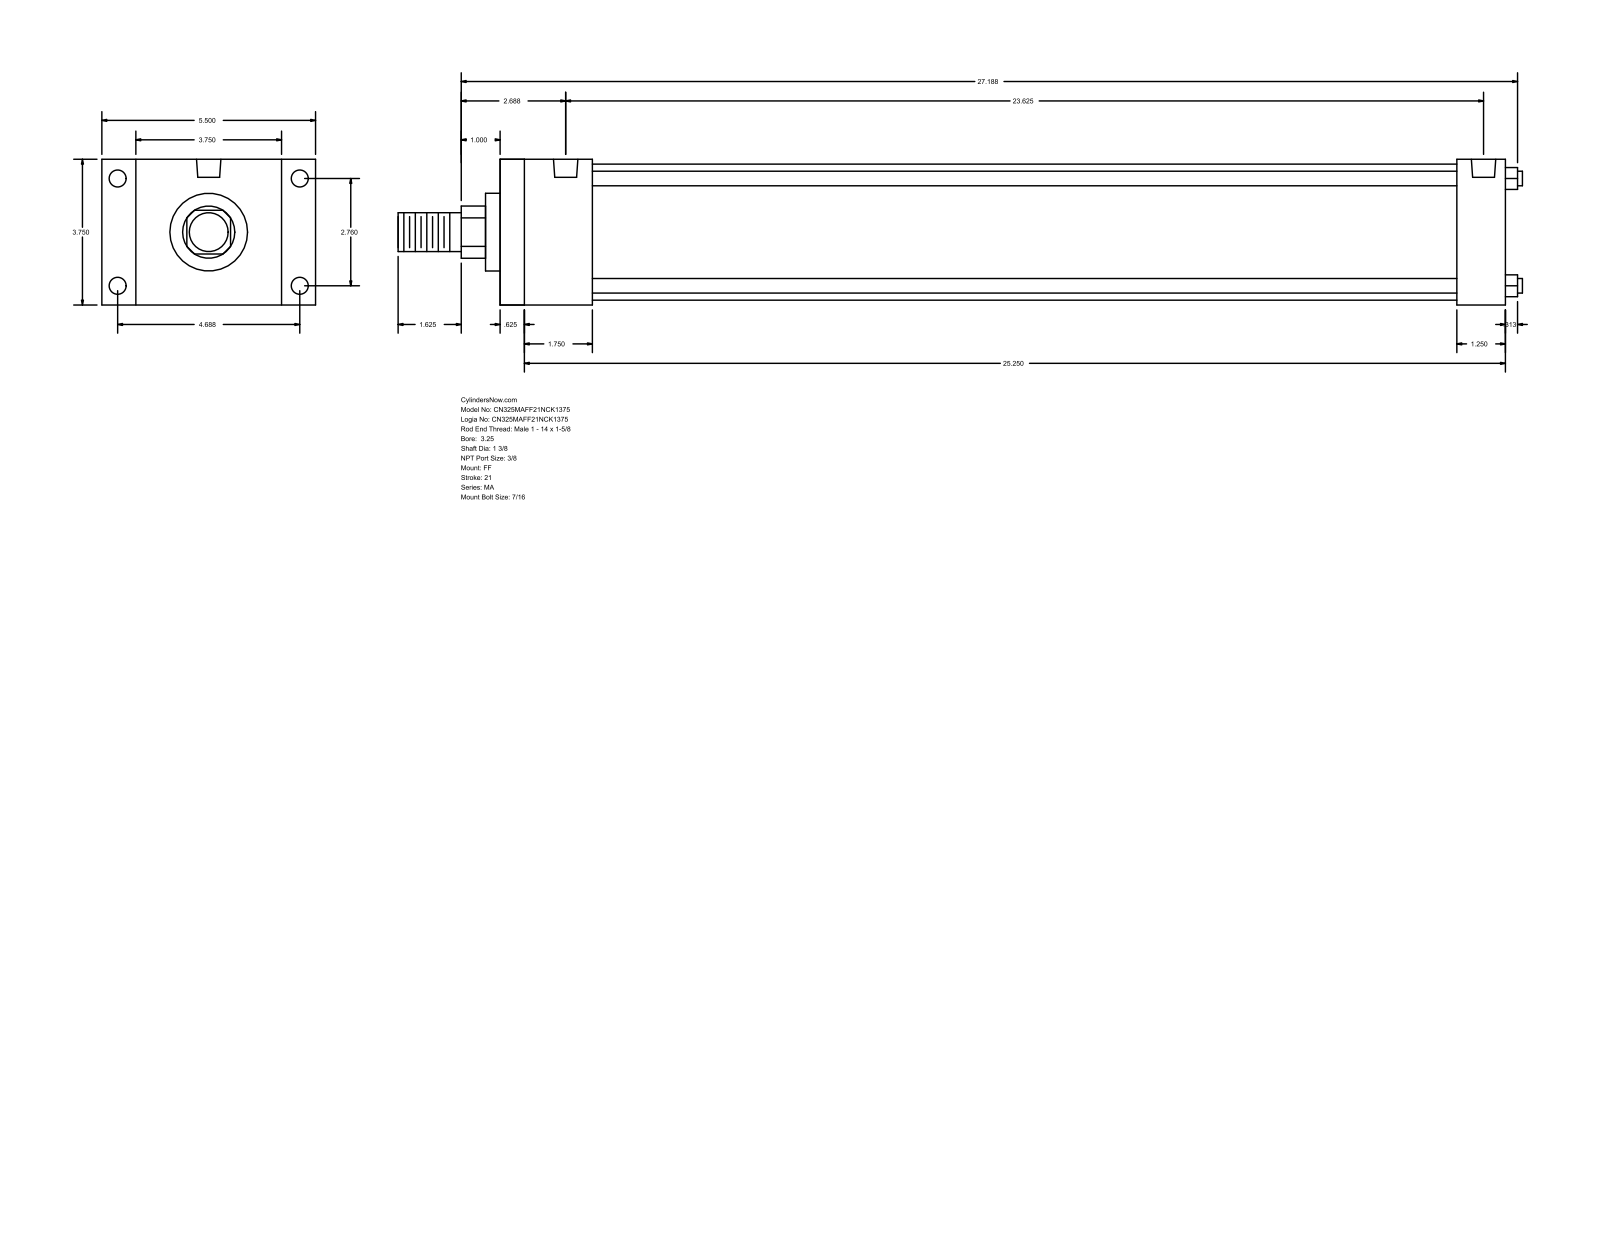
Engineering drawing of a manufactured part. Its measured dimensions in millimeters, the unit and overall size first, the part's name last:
Units: millimetres
Overall size (bounding box): 735.01 × 139.7 × 95.25
Round holes (diameter × count): ⌀11.11 ×8, ⌀15.93 ×2
Round bosses / shafts (diameter × count): ⌀9.53 ×4, ⌀88.9 ×1, ⌀50.8 ×1, ⌀34.92 ×1, ⌀25.4 ×1
Partial cylindrical surfaces — rounded edges, fillets, slot ends (radius × count): R17.06 ×1
Main face-to-face distances: 95.24, 657.22, 15.87, 641.35, 22.23, 117.47, 60.32, 625.48, 44.45, 609.61
Hole centre spacings: 70.1, 119.06, 138.16, 590.55, 4.76, 4.77, 595.31, 595.32
Bodies: 0 solids, 92 faces (64 planar, 28 cylindrical, 0 other)
Part name (STEP PRODUCT): MA_FF__0325_1.375
STEP written by: GSSL Pune (CONFIG_CONTROL_DESIGN)
